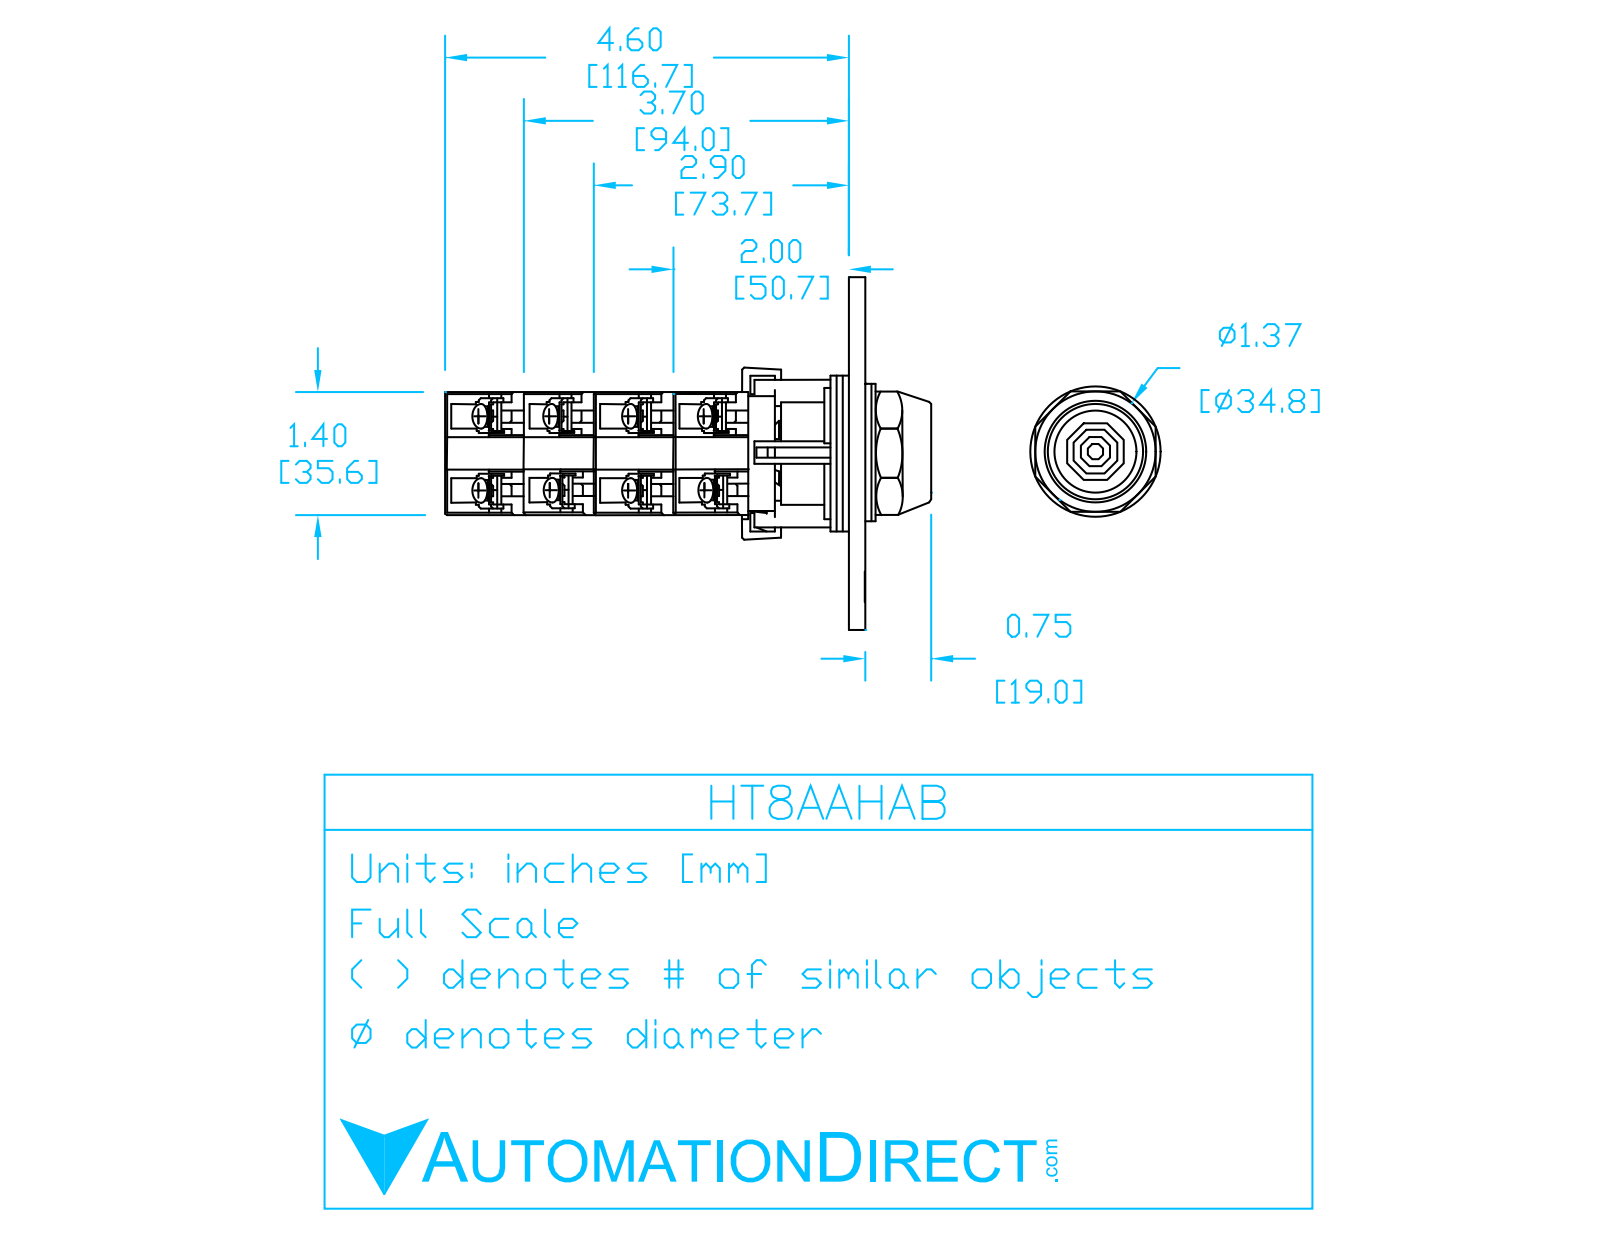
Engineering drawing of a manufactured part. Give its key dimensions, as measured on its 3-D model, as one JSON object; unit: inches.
{"part_name": "HT8ABGF1Q1", "step_written_by": "SolidWorks 2017 (AUTOMOTIVE_DESIGN)", "units": "inches", "bodies": {"solids": 43, "faces": 925, "planar": 631, "cylindrical": 237, "other": 57}, "overall_size": [3.935, 1.969, 1.969], "volume_in3": 6.36, "surface_area_in2": 94.66, "round_holes": [[0.126, 16], [0.157, 2], [0.161, 2], [0.165, 2], [0.305, 2], [0.689, 1], [0.945, 1], [0.965, 1], [1.201, 1], [1.22, 1]], "round_bosses_or_shafts": [[0.244, 8], [0.118, 8], [0.276, 2], [0.252, 2], [0.157, 2], [1.732, 1], [1.496, 1], [1.181, 1]], "partial_cylinders_radius": [[0.039, 18], [0.069, 8], [0.02, 4], [0.128, 4], [0.13, 2], [0.148, 2], [0.827, 1], [0.874, 1]], "face_to_face_distances": [0.063, 0.126, 0.866, 0.189, 0.886, 0.909, 0.059, 0.252, 0.972, 0.394], "hole_center_spacings": [0.886, 0.426, 0.426, 0.983, 0.983, 0.719, 1.016, 1.437]}
